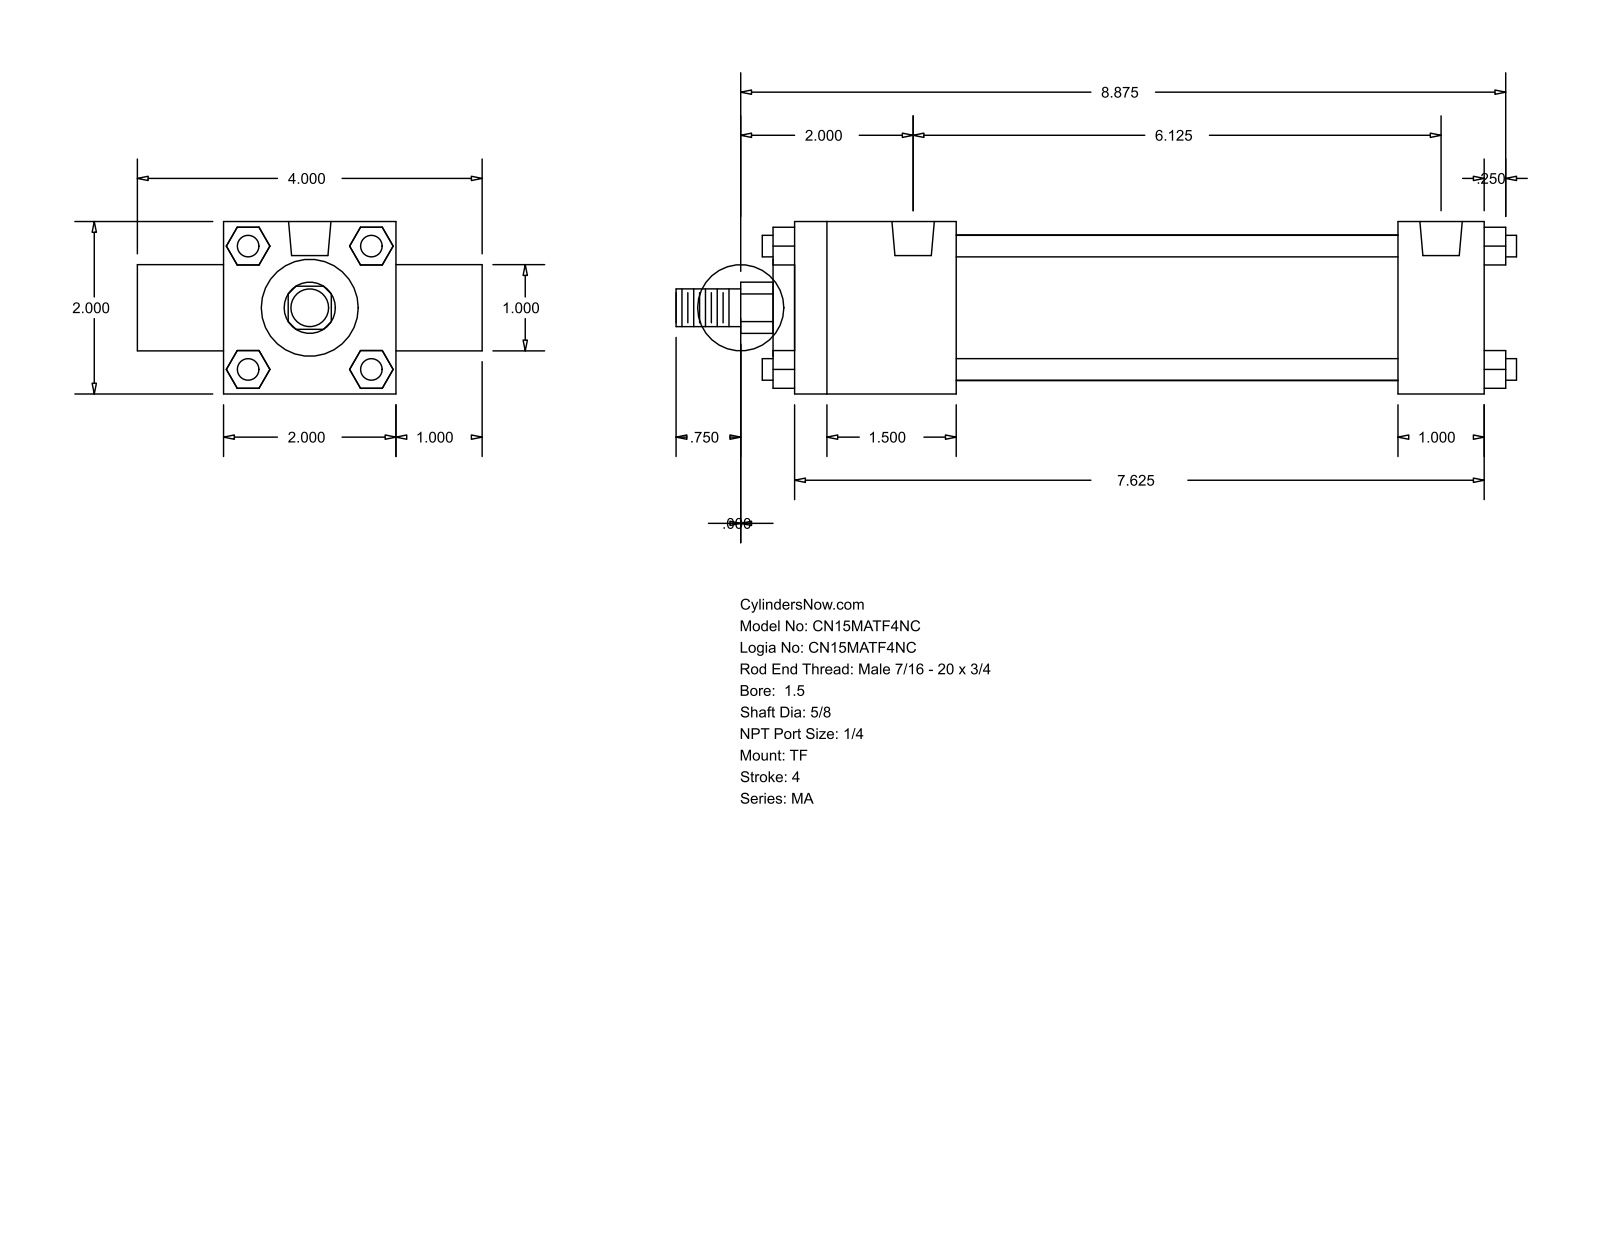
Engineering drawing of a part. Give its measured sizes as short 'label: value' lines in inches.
name: MA_TF__0150_0.625
written by: GSSL Pune (CONFIG_CONTROL_DESIGN)
unit: in
bodies: 0 solids, 120 faces (92 planar, 28 cylindrical, 0 other)
size: 9.75 × 4 × 2
holes: 3× ⌀0.313, 2× ⌀0.492
bosses: 4× ⌀0.25, 1× ⌀1.69, 1× ⌀1.125, 1× ⌀1, 1× ⌀0.625, 1× ⌀0.437
rounds: 1× R0.297
face distances: 2, 8, 1, 3, 1.875, 7, 5.125, 6.125, 1, 0.25
hole spacings: 6.125
